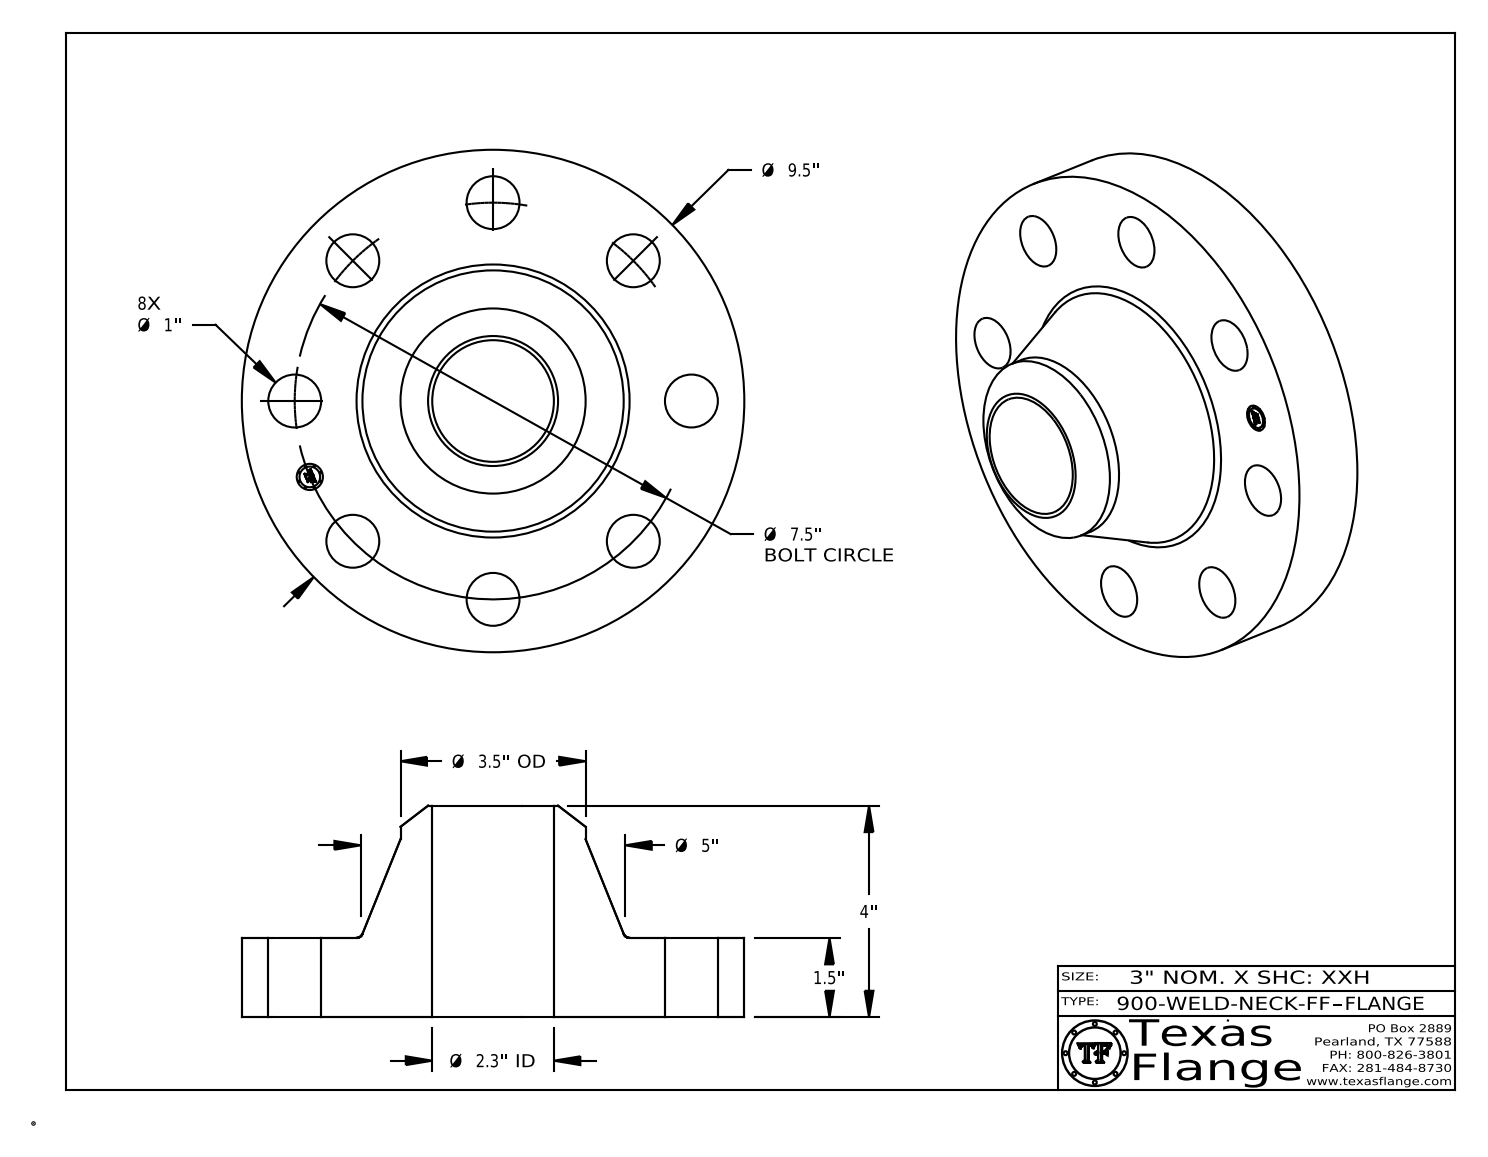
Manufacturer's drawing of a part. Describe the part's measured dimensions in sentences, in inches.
The part is named "900-WELD-NECK-FF". Its 3-D file was written by "CATIA V5 STEP AP214 (AUTOMOTIVE_DESIGN)". It is 1 solid with 416 faces: 368 planar, 42 cylindrical and 6 other. Overall it measures 9.5 by 9.5 by 4 inches. Its volume is 112.1 cubic inches and its surface area 252.7 square inches. Round holes: 8 of diameter 1, 1 of diameter 0.495, 1 of diameter 2.3. Round bosses or shafts: 8 of diameter 0.03, 1 of diameter 9.5, 1 of diameter 3.5, 1 of diameter 0.39. The main face-to-face distances are 1.5, 4, 2.5, 0.015, 1.485, 2.515, 0.148, 0.145, 0.027, 0.096. The hole center spacings are 3.75, 2.87, 5.303, 6.929, 1.463, 6.236, 7.356, 7.5.
